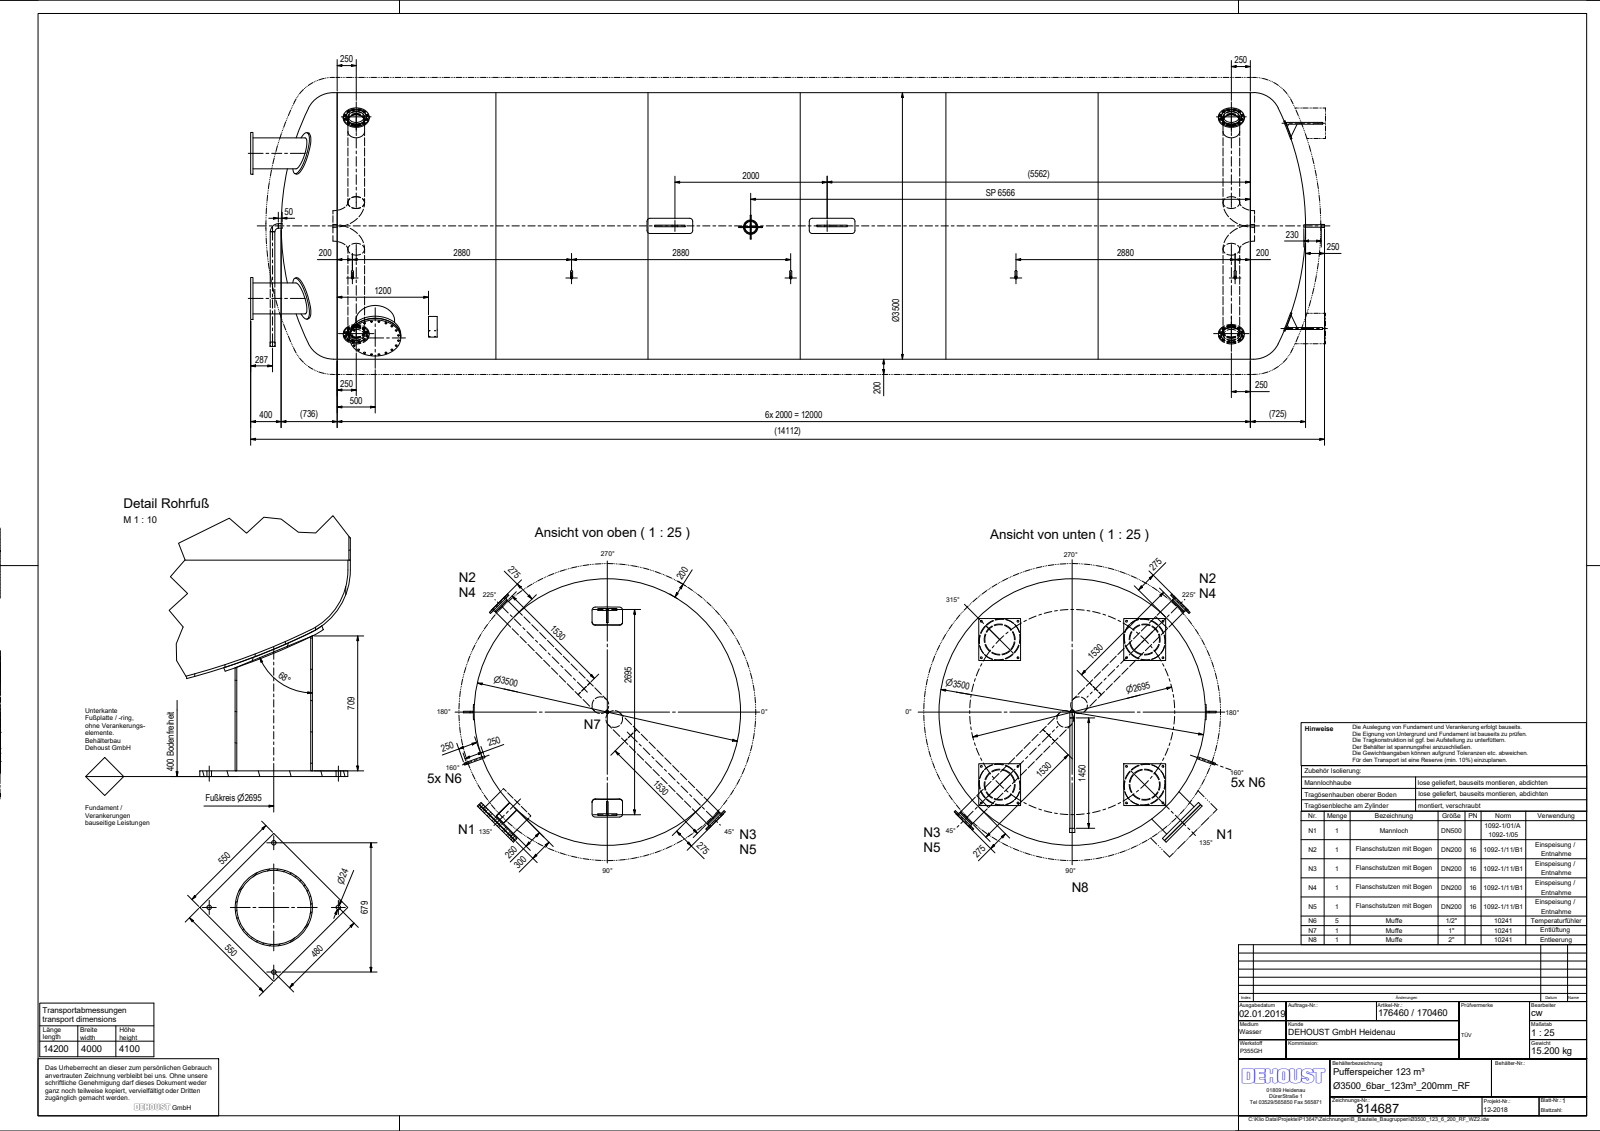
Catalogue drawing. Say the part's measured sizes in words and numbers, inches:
The part is named "Ø3500_123_6_200_RF_WZ2; Klöpper_Gew_Ø3500_10,6; Klöpper_Gew_Ø3500_13,0; Zyl_Ø3500_8x12000_2019 (+8 more)". Its 3-D file was written by "Autodesk Inventor 2019 (AUTOMOTIVE_DESIGN)". It is 58 solids with 453 faces: 176 planar, 231 cylindrical and 46 other. Overall it measures 555.576 by 143.386 by 137.795 inches. Its volume is 111 500 cubic inches and its surface area 533 500 square inches. Round holes: 48 of diameter 0.866, 40 of diameter 1.024, 16 of diameter 0.945, 5 of diameter 0.733, 5 of diameter 0.854, 5 of diameter 1.059, 4 of diameter 0.228, 4 of diameter 8.13, 4 of diameter 8.161, 4 of diameter 8.626, 4 of diameter 15.307, 2 of diameter 2.059. Round bosses or shafts: 8 of diameter 8.626, 5 of diameter 1.059, 5 of diameter 1.039, 4 of diameter 22.047, 4 of diameter 16, 4 of diameter 13.386, 4 of diameter 10.551, 2 of diameter 26.378. Partial cylindrical surfaces (rounded edges, fillets, slot ends): 8 of radius 1.575, 8 of radius 1.654, 2 of radius 0.197, 2 of radius 0.394, 2 of radius 2.835, 1 of radius 4.921, 1 of radius 69.37. The main face-to-face distances are 1.181, 23.622, 218.701, 253.74, 263.438, 298.478, 262.257, 297.296, 35.039, 1.102. The hole center spacings are 12.205, 5.807, 7.543, 21.749, 113.386, 23.215, 5.807, 10.058.
